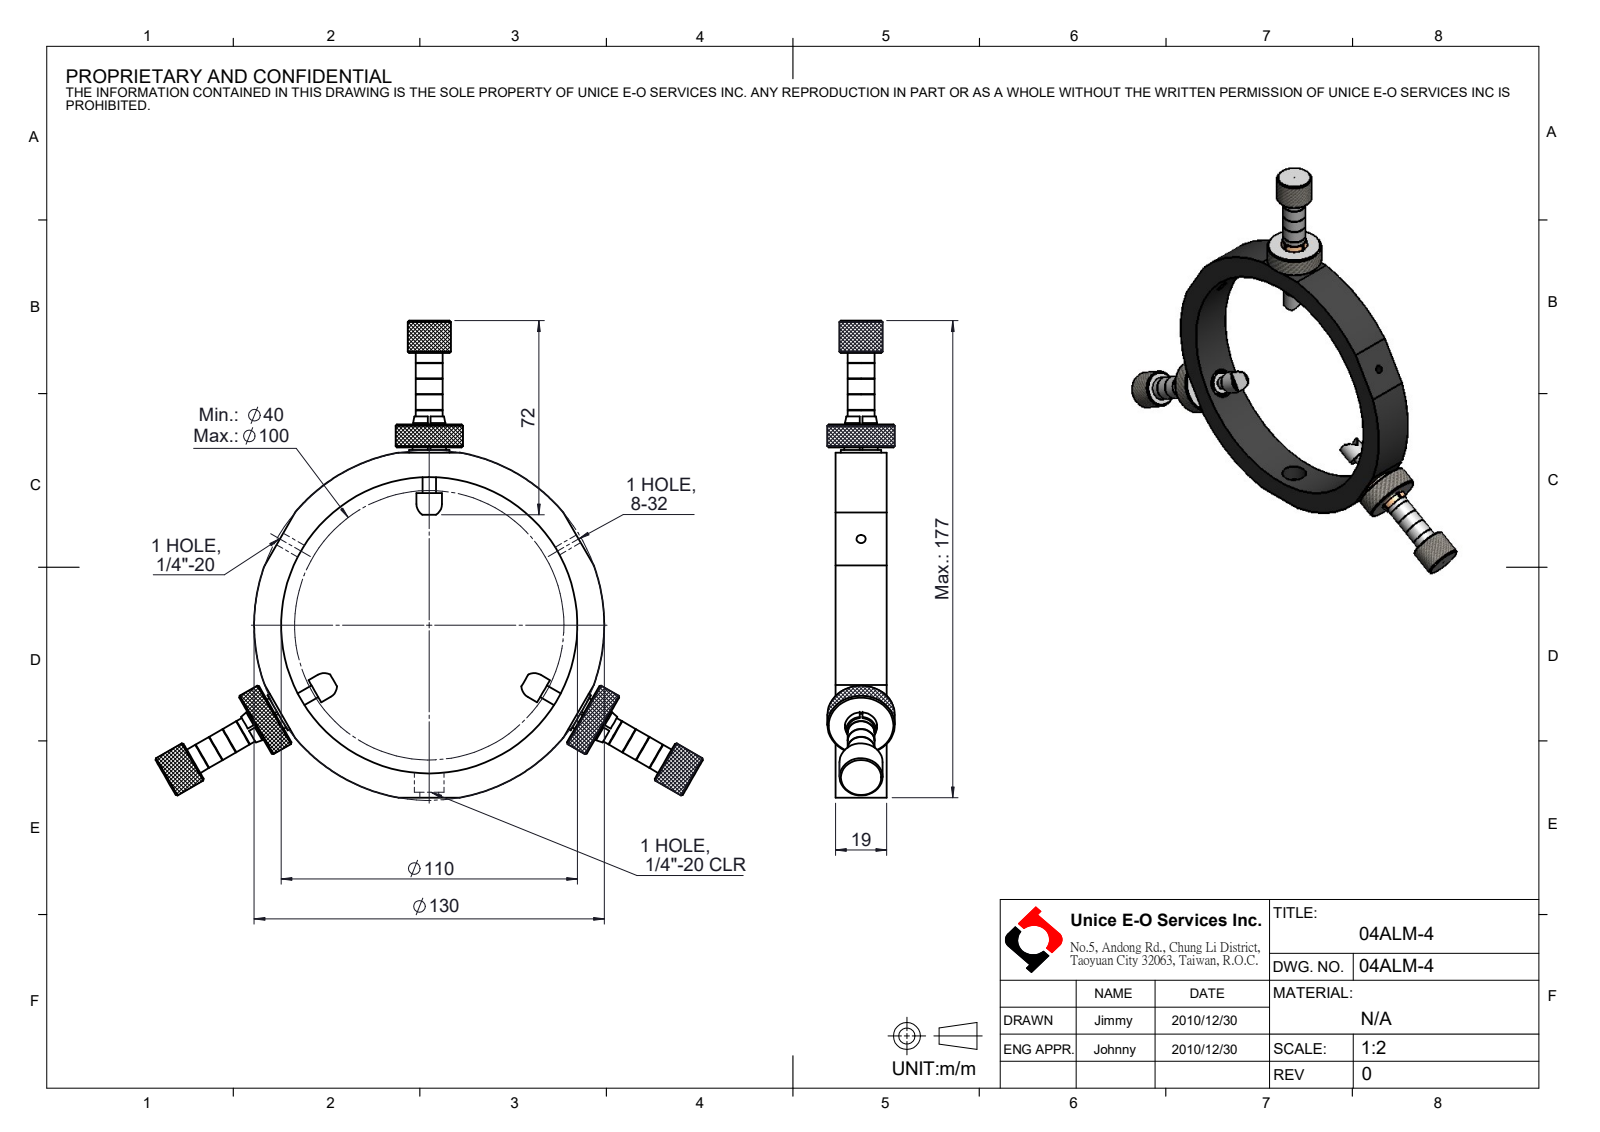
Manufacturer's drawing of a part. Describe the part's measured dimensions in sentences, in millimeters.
The part is named "04ALM-4". Its 3-D file was written by "SolidWorks 2016 (CONFIG_CONTROL_DESIGN)". It is 16 solids with 469 faces: 171 planar, 238 cylindrical and 60 other. Overall it measures 203.22 by 177 by 25 millimeters. Its volume is 95 255 cubic millimeters and its surface area 50 311 square millimeters. Round holes: 3 of diameter 5.25, 3 of diameter 8, 3 of diameter 11, 3 of diameter 12.7, 1 of diameter 3.45, 1 of diameter 5.11, 1 of diameter 7, 1 of diameter 110. Round bosses or shafts: 3 of diameter 25, 3 of diameter 16, 3 of diameter 15, 3 of diameter 12.5, 3 of diameter 12, 3 of diameter 10, 3 of diameter 9.5, 3 of diameter 9. Partial cylindrical surfaces (rounded edges, fillets, slot ends): 1 of radius 65. The main face-to-face distances are 19, 2, 8.5, 10.5, 128, 138.5, 130, 38.5, 47, 10.
